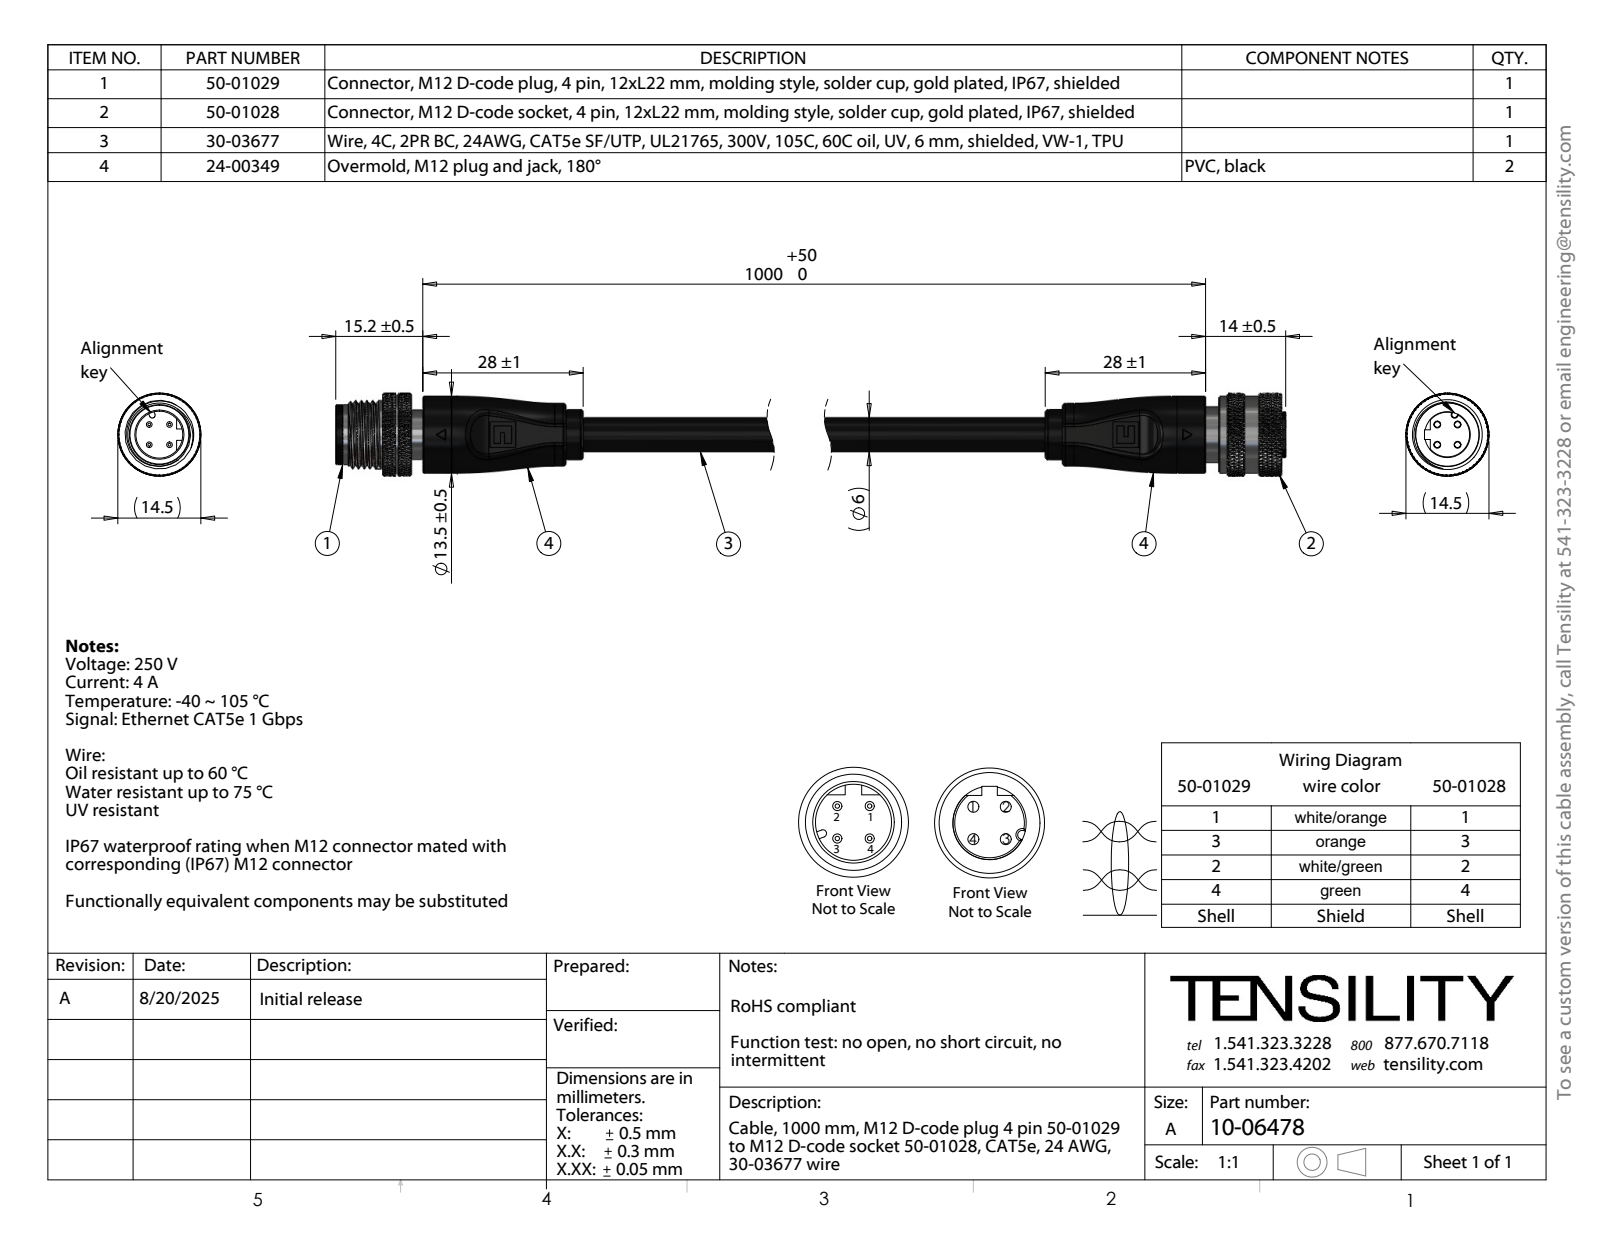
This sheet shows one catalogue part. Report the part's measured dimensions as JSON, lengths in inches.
{"part_name": "50-01028-04_默认; 50-01028-03_默认; 10-06478; 50-01029_默认 (+8 more)", "step_written_by": "SolidWorks 2025 (CONFIG_CONTROL_DESIGN)", "units": "inches", "bodies": {"solids": 53, "faces": 5792, "planar": 362, "cylindrical": 1477, "other": 3953}, "overall_size": [9.26, 0.571, 0.571], "volume_in3": 0.838, "surface_area_in2": 47.49, "round_holes": [[0.008, 28], [0.039, 4], [0.041, 4], [0.043, 4], [0.047, 4], [0.124, 1], [0.126, 1], [0.14, 1], [0.323, 1], [0.374, 1], [0.394, 1], [0.441, 1]], "round_bosses_or_shafts": [[0.063, 4], [0.059, 4], [0.055, 4], [0.571, 1], [0.547, 1], [0.531, 1], [0.472, 1], [0.433, 1]], "partial_cylinders_radius": [[0.004, 10], [0.016, 6], [0.02, 4], [0.059, 2], [0.077, 2], [0.197, 2], [0.22, 1], [0.266, 1]], "face_to_face_distances": [8.11, 0.276, 1.102, 7.008, 0.079, 8.189, 0.15, 8.339, 8.201, 0.228], "hole_center_spacings": [0.075, 0.014, 0.082, 0.042, 0.035, 0.043, 0.049, 0.071]}
